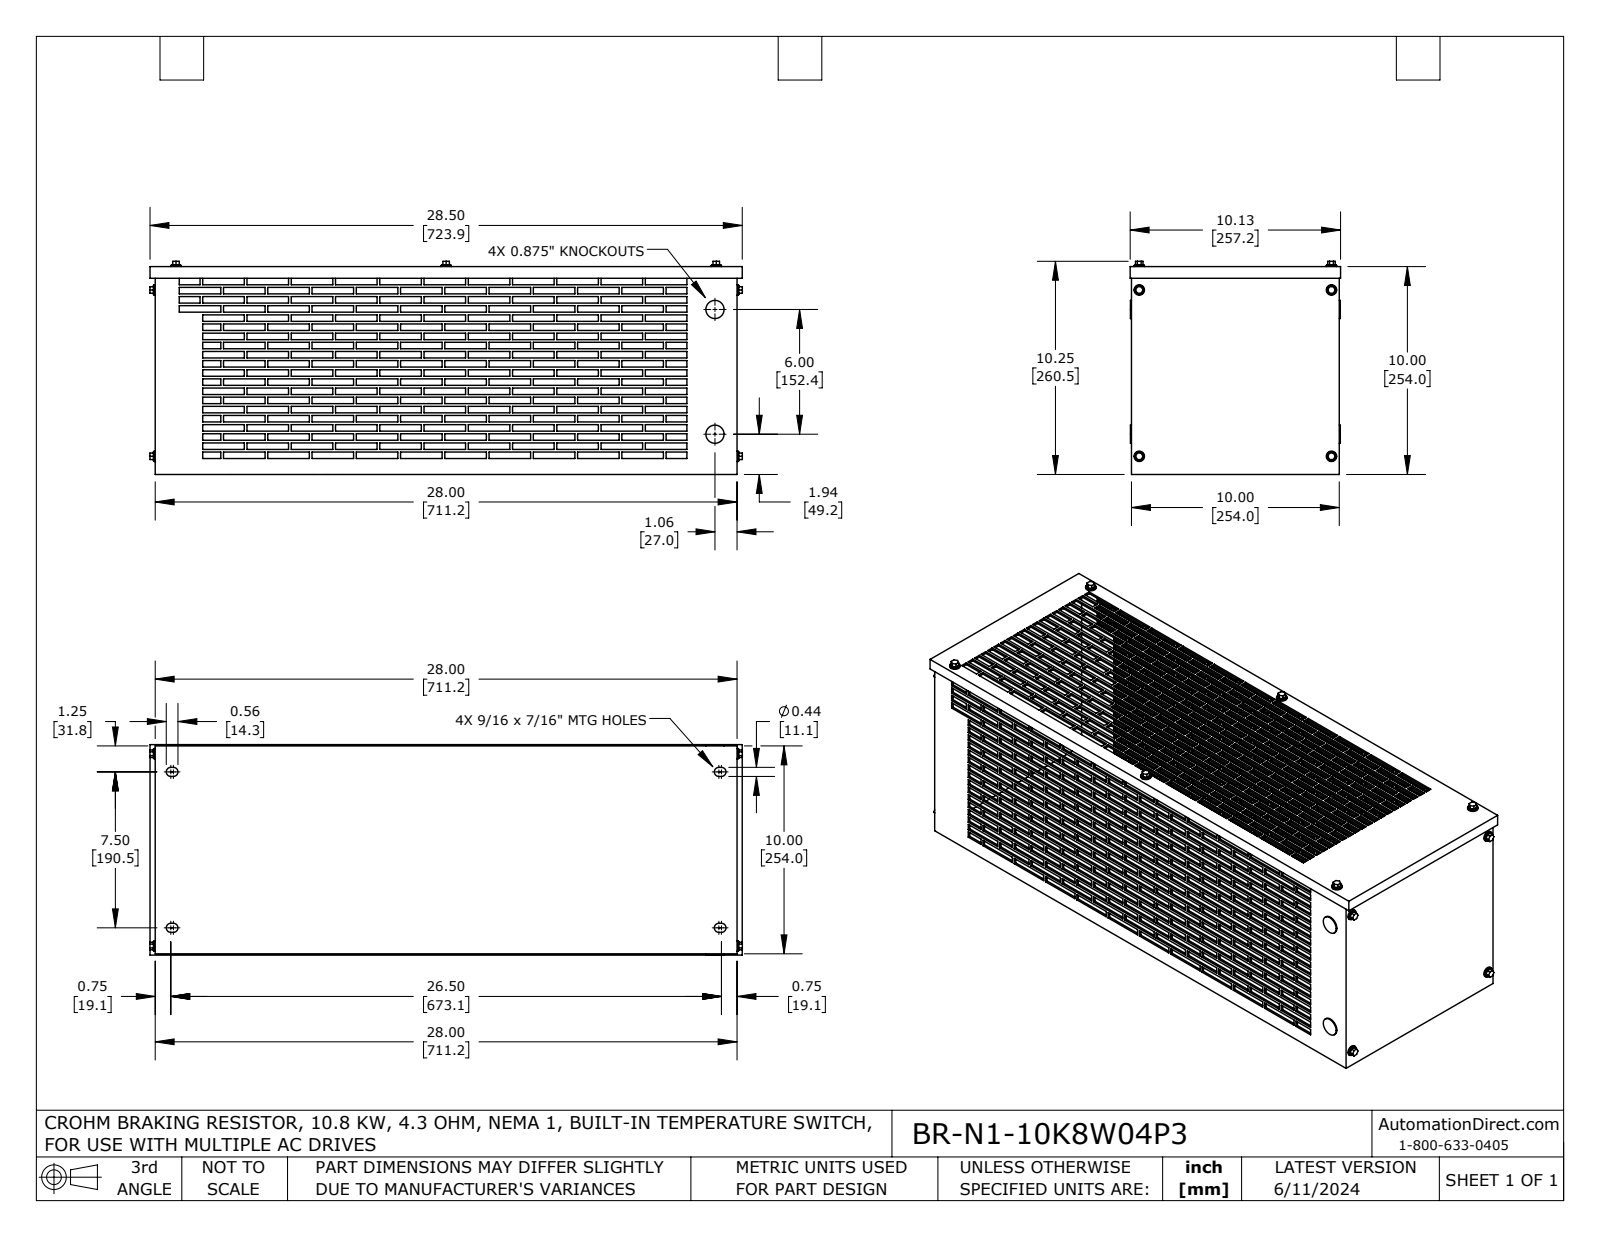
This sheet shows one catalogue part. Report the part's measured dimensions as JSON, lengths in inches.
{"part_name": "BR-N1-10K8W04P3", "step_written_by": "SolidWorks 2021 (AUTOMOTIVE_DESIGN)", "units": "inches", "bodies": {"solids": 33, "faces": 3056, "planar": 2948, "cylindrical": 108, "other": 0}, "overall_size": [28.509, 10.254, 10.125], "volume_in3": 90.75, "surface_area_in2": 2134, "round_holes": [[0.25, 10], [0.75, 2]], "round_bosses_or_shafts": [[0.5, 10], [0.437, 10], [0.875, 2]], "partial_cylinders_radius": [[0.219, 8]], "face_to_face_distances": [0.1, 9.9, 10, 9.8, 27.9, 28, 27.8, 0.063, 9.963, 0.88], "hole_center_spacings": [9.25, 13, 15.955, 8, 12.229, 26, 27.596, 6]}
